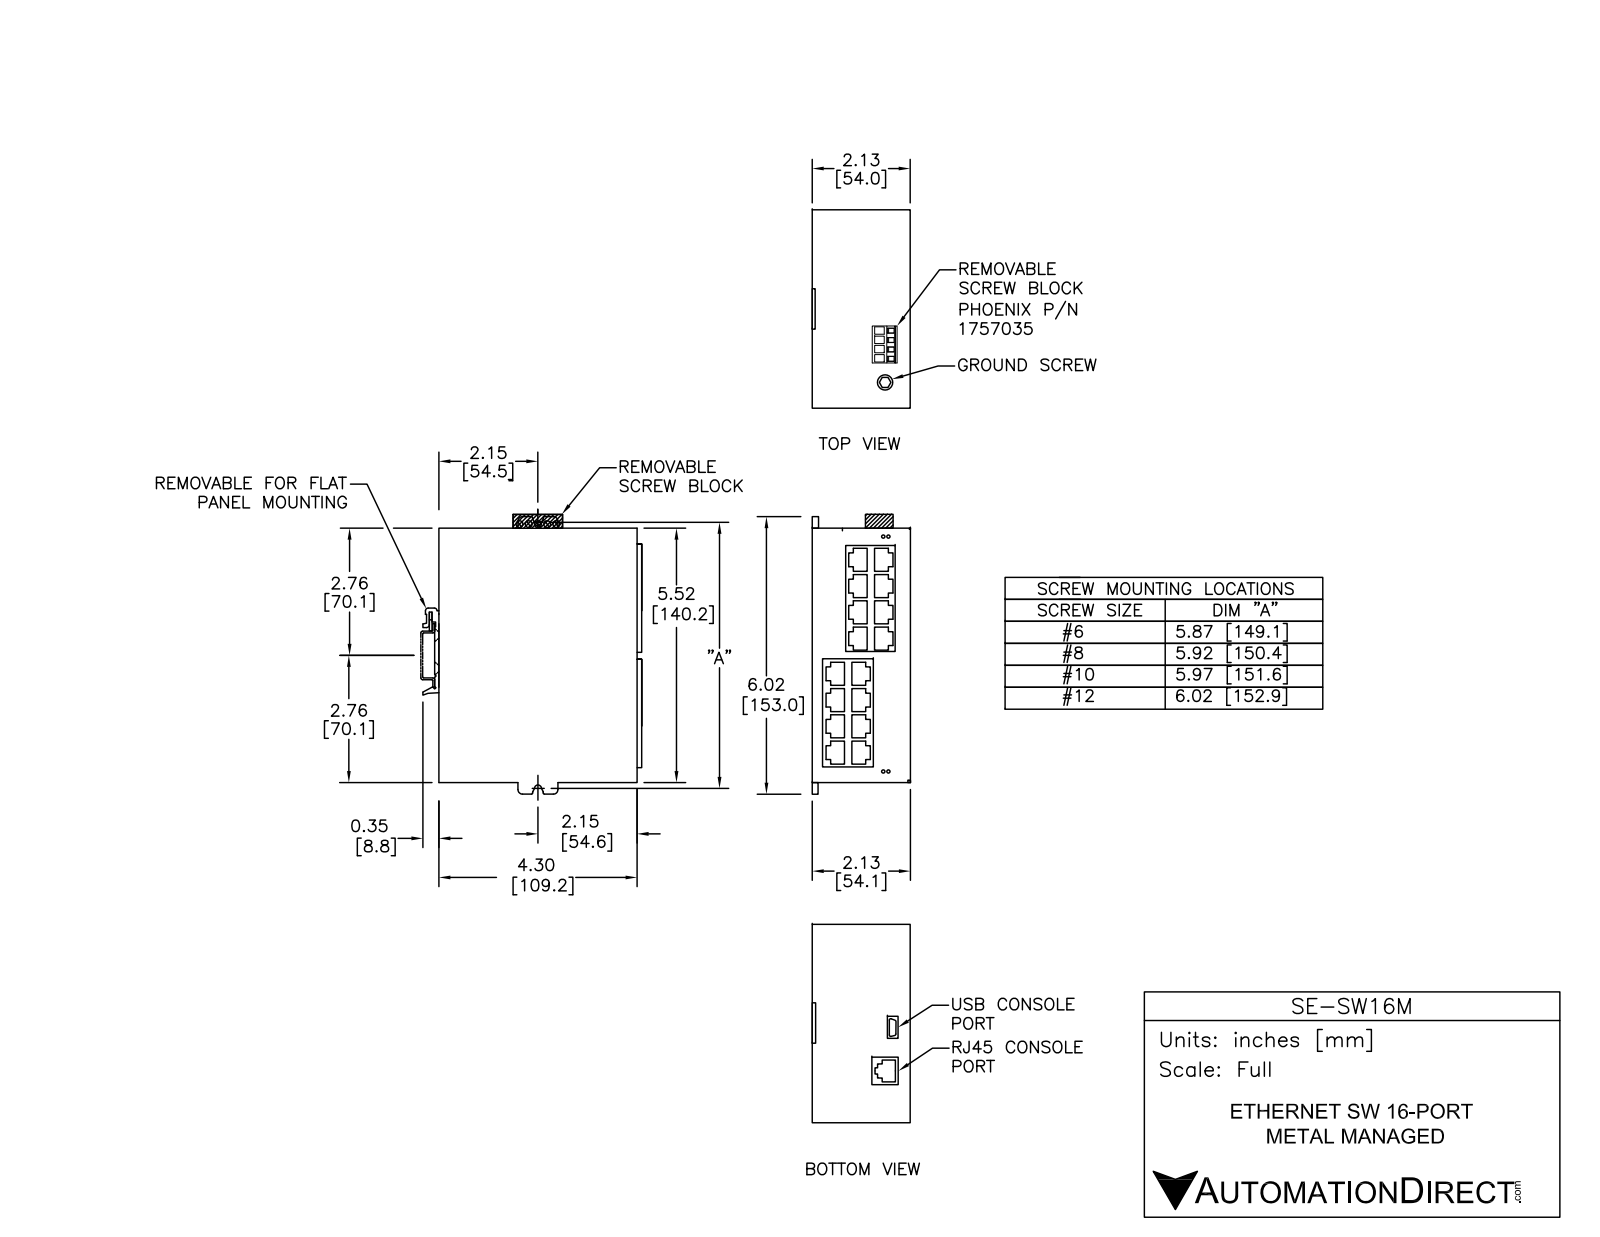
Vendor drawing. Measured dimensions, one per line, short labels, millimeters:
name: SE-SW16M
written by: SolidWorks 2011 (AUTOMOTIVE_DESIGN)
unit: mm
bodies: 1 solid, 472 faces (428 planar, 44 cylindrical, 0 other)
size: 157.7 × 119.6 × 54.4
volume: 831 600 mm³; area: 110 600 mm²
holes: 4× ⌀2.8, 4× ⌀3.5, 1× ⌀6.1
bosses: 1× ⌀8.5
rounds: 8× R0.4, 6× R0.6, 4× R1.5, 4× R2.5, 2× R0.2, 2× R0.8, 2× R1.8, 1× R2
face distances: 1.5, 54.4, 1.5, 52.8, 52.9, 1.5, 140.5, 109.2, 107.7, 107.7
hole spacings: 4.7, 6.6, 9.4, 131.5, 131.6, 14.1
